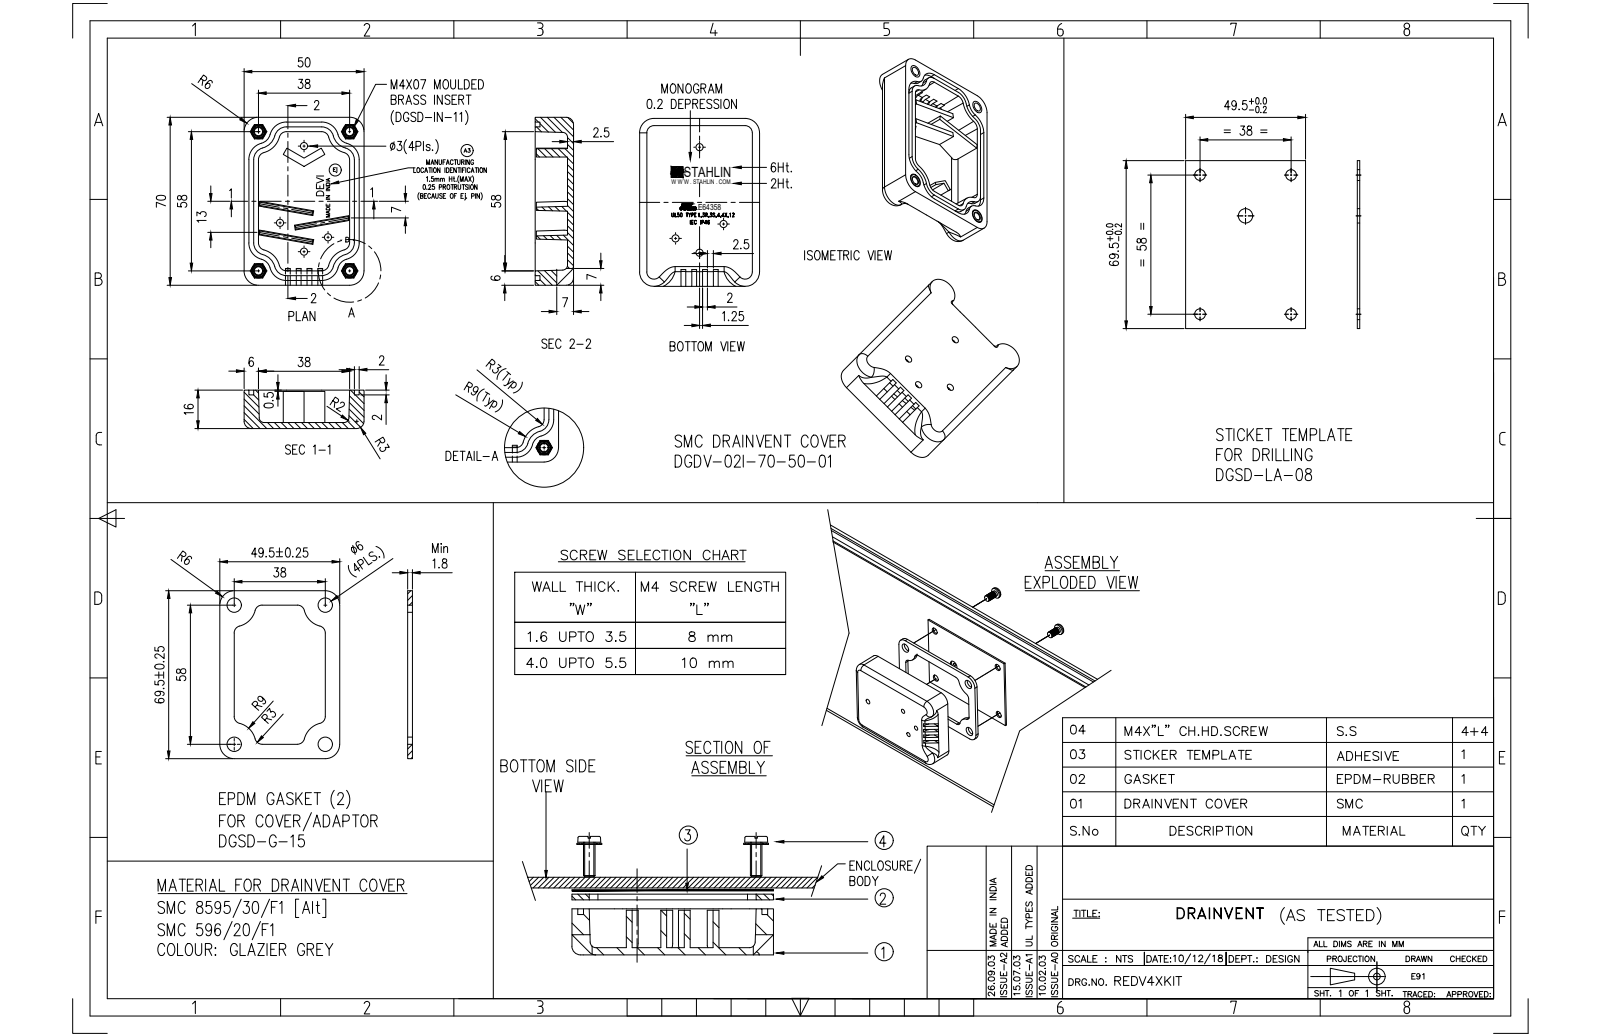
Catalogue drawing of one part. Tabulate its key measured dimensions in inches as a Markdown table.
| quantity | value |
| --- | --- |
| part name | REDV4XKIT |
| STEP written by | SolidWorks 2017 (AUTOMOTIVE_DESIGN) |
| units | inches |
| bodies | 10 solids, 1377 faces (1050 planar, 117 cylindrical, 210 other) |
| overall size | 2.756 × 1.969 × 1.116 |
| volume | 2.008 in³ |
| surface area | 34.73 in² |
| round holes (diameter × count) | 0.13 × 4, 0.187 × 4, 0.197 × 4, 0.125 × 3, 0.01 × 1, 0.125 × 1 |
| round bosses / shafts (diameter × count) | 0.236 × 4, 0.157 × 4 |
| partial cylindrical surfaces (radius × count) | 0.02 × 27, 0.197 × 8, 0.275 × 8, 0.071 × 6, 0.007 × 5, 0.197 × 4, 0.236 × 4, 0.276 × 4 |
| main face-to-face distances | 0.63, 0.059, 0.571, 0.079, 0.709, 0.65, 1.969, 0.079, 0.158, 0.551 |
| hole center spacings | 1.496, 2.283, 2.73, 0.406, 0.465, 0.668, 0.676, 0.793 |
